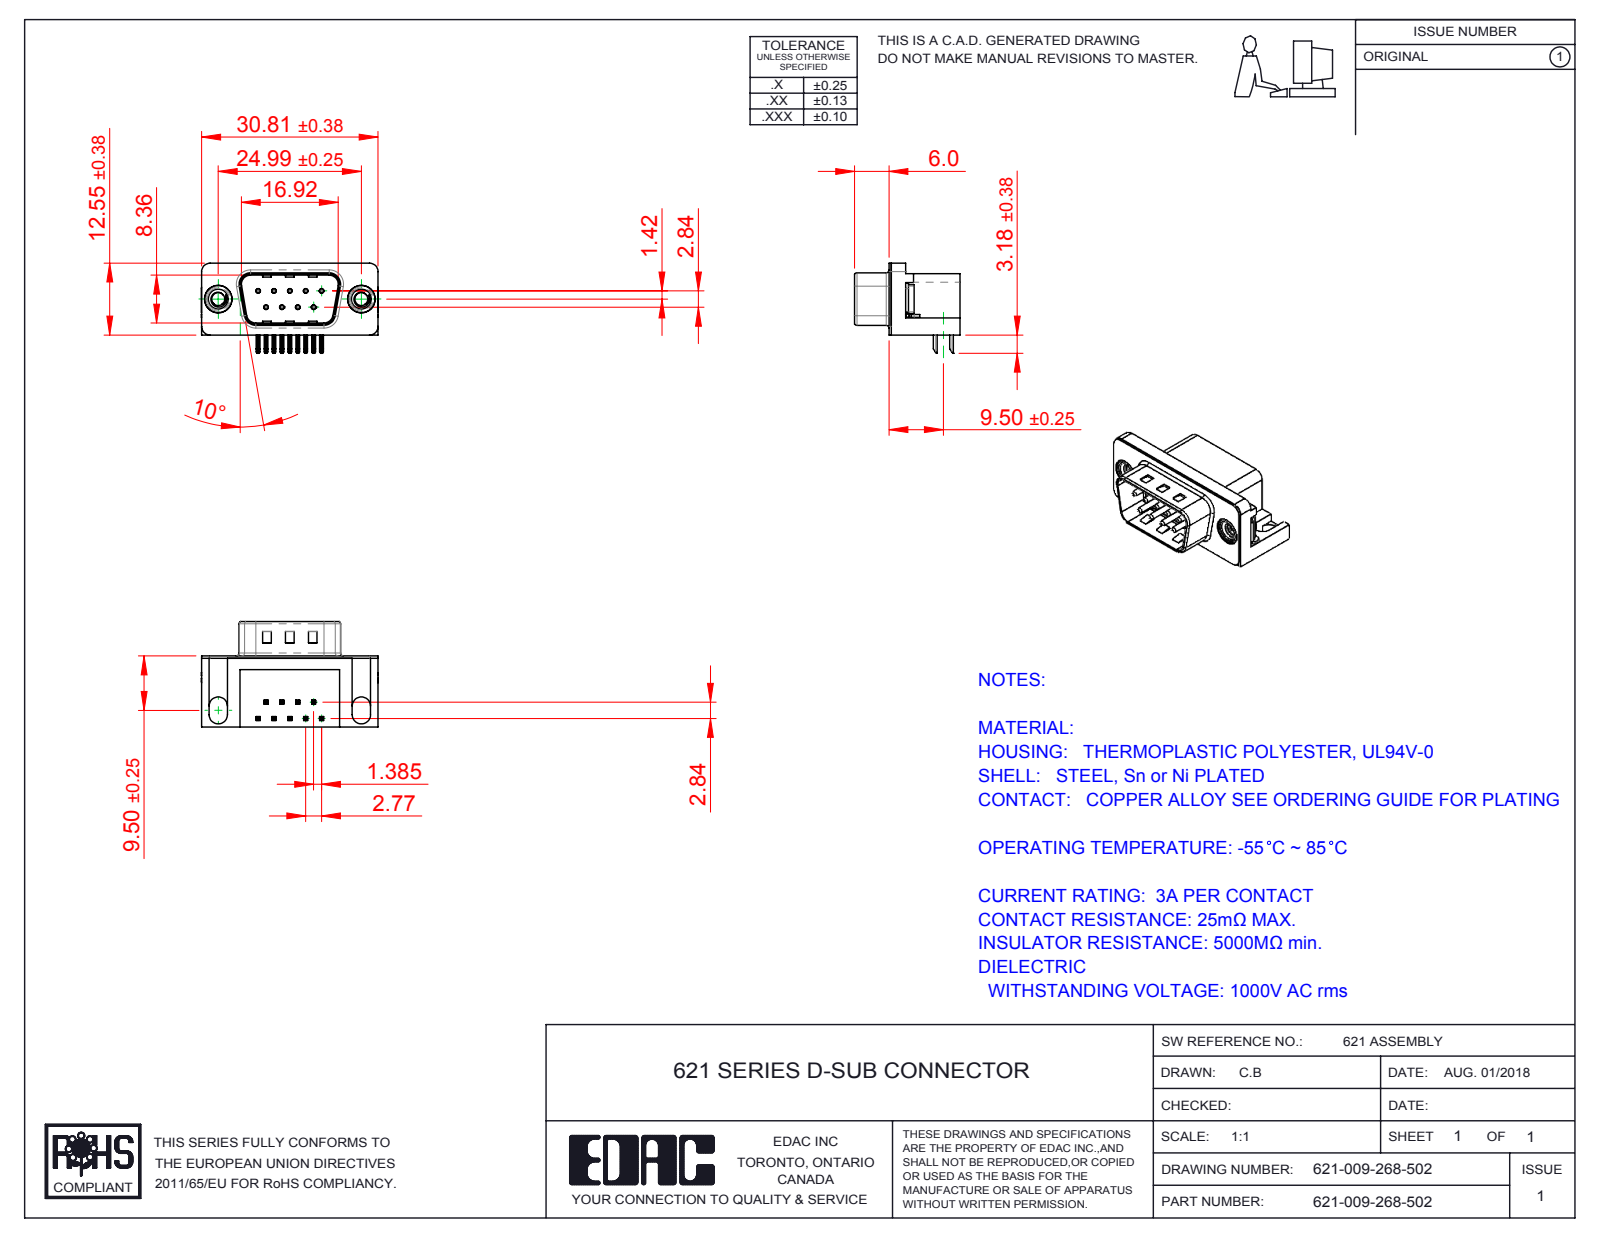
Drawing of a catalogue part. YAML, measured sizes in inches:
part_name: "621-009-268-502; 621 4-40 Threaded Rivet; 621 Contact Bottom; 621 Contact Top (+3 more)"
step_written_by: "SolidWorks 2016 (CONFIG_CONTROL_DESIGN)"
units: inches
bodies: {solids: 15, faces: 985, planar: 571, cylindrical: 311, other: 103}
overall_size: [1.216, 0.724, 0.619]
volume: 0.196
surface_area: 6.584
round_holes:
  - {diameter: 0.014, count: 9}
  - {diameter: 0.031, count: 9}
  - {diameter: 0.089, count: 2}
  - {diameter: 0.157, count: 2}
  - {diameter: 0.189, count: 2}
  - {diameter: 0.197, count: 2}
round_bosses_or_shafts:
  - {diameter: 0.03, count: 9}
  - {diameter: 0.193, count: 2}
  - {diameter: 0.187, count: 2}
  - {diameter: 0.154, count: 2}
partial_cylinders:
  - {radius: 0.01, count: 44}
  - {radius: 0.005, count: 18}
  - {radius: 0.039, count: 16}
  - {radius: 0.02, count: 9}
  - {radius: 0.059, count: 8}
  - {radius: 0.063, count: 8}
  - {radius: 0.035, count: 4}
  - {radius: 0.079, count: 4}
face_to_face_distances: [0.016, 0.472, 0.488, 0.407, 0.114, 0.374, 0.098, 0.083, 0.014, 0.421]
hole_center_spacings: [0.124, 0.109, 0.218, 0.198, 0.198, 0.327, 0.294, 0.295]
